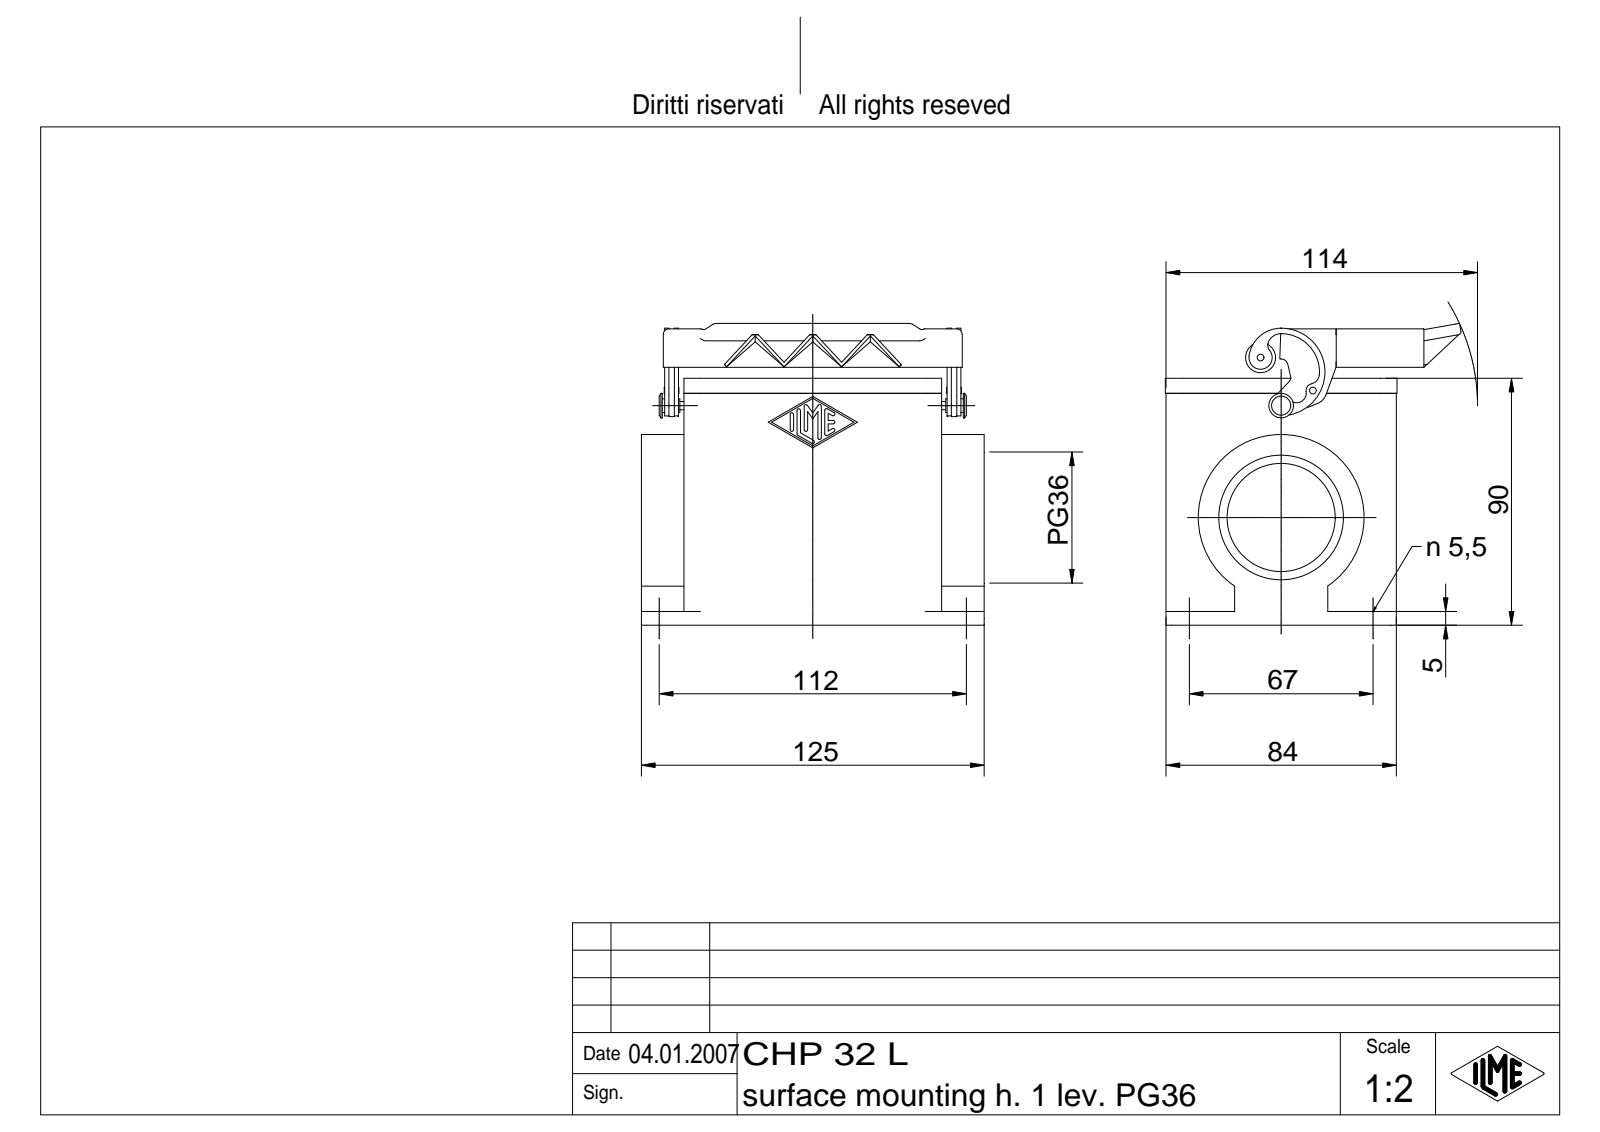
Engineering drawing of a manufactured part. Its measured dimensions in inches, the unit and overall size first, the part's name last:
Units: inches
Overall size (bounding box): 4.921 × 4.33 × 4.246
Round holes (diameter × count): ⌀0.217 ×4, ⌀0.079 ×1, ⌀1.554 ×1, ⌀1.791 ×1
Round bosses / shafts (diameter × count): ⌀2.382 ×1, ⌀0.433 ×1, ⌀0.354 ×1, ⌀0.197 ×1, ⌀0.118 ×1, ⌀0.098 ×1
Partial cylindrical surfaces — rounded edges, fillets, slot ends (radius × count): R0.079 ×16, R0.024 ×14, R0.059 ×9, R0.236 ×8, R0.006 ×4, R0.118 ×4, R0.039 ×3, R0.098 ×3
Main face-to-face distances: 0.118, 3.189, 3.307, 0.157, 0.453, 3.071, 3.248, 2.795, 3.858, 3.327
Hole centre spacings: 2.638, 4.409, 5.138, 1.878
Volume: 15.68 in³ · Surface area: 165.1 in²
Bodies: 4 solids, 491 faces (166 planar, 145 cylindrical, 180 other)
Part name (STEP PRODUCT): CHP 32 L
STEP written by: Autodesk Inventor 7 (AUTOMOTIVE_DESIGN)
